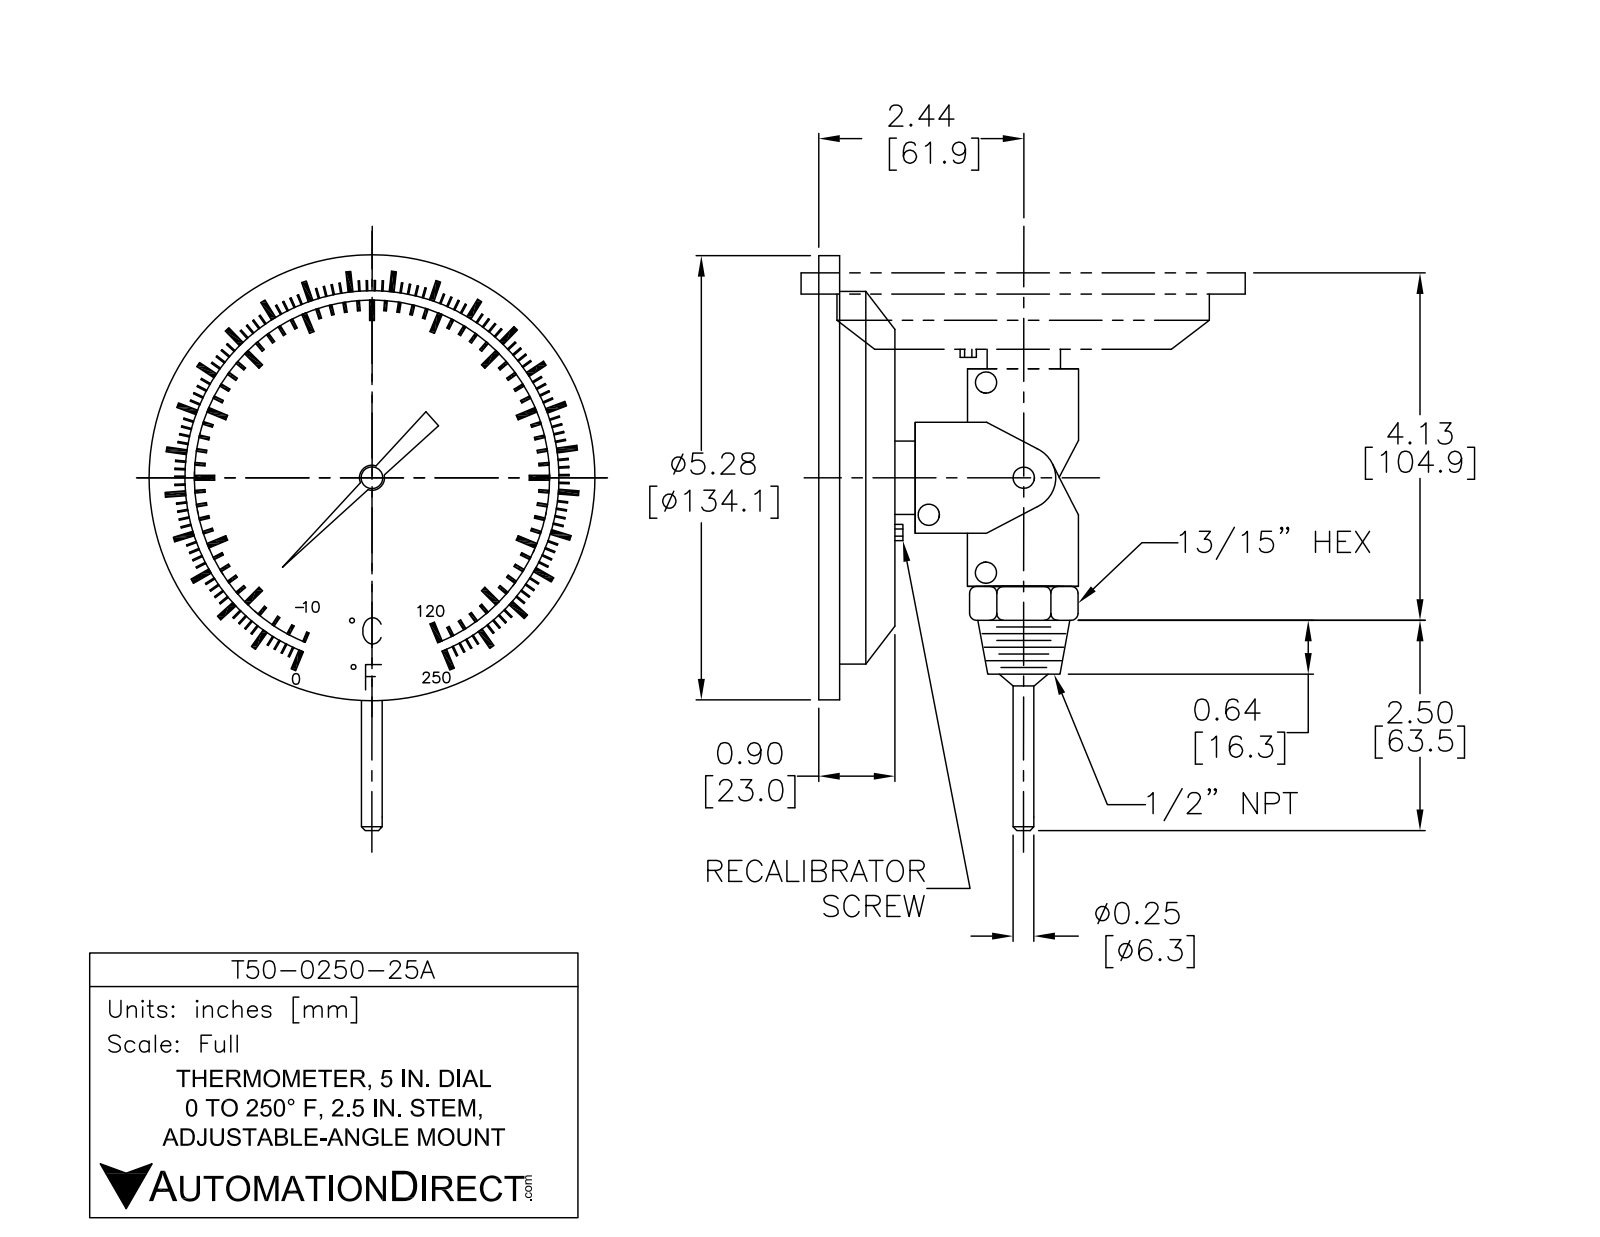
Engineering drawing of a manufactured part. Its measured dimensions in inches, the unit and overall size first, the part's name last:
Units: inches
Overall size (bounding box): 6.46 × 5.28 × 5.28
Round holes (diameter × count): ⌀3.424 ×1, ⌀3.7 ×1, ⌀4.76 ×1, ⌀4.836 ×1
Round bosses / shafts (diameter × count): ⌀0.305 ×4, ⌀0.145 ×2, ⌀5.28 ×1, ⌀4.97 ×1, ⌀3.73 ×1, ⌀3.454 ×1, ⌀0.85 ×1, ⌀0.822 ×1
Partial cylindrical surfaces — rounded edges, fillets, slot ends (radius × count): R0.06 ×10, R0.04 ×4, R0.17 ×1, R0.336 ×1, R0.336 ×1, R0.342 ×1, R0.4 ×1
Main face-to-face distances: 0.353, 0.074, 0.055, 0.427, 1.19, 0.815, 0.462, 0.388, 1.245, 2.435
Volume: 10.06 in³ · Surface area: 95.62 in²
Bodies: 1 solid, 481 faces (277 planar, 45 cylindrical, 159 other)
Part name (STEP PRODUCT): T50-0250-25A
STEP written by: SolidWorks 2021 (AUTOMOTIVE_DESIGN)
